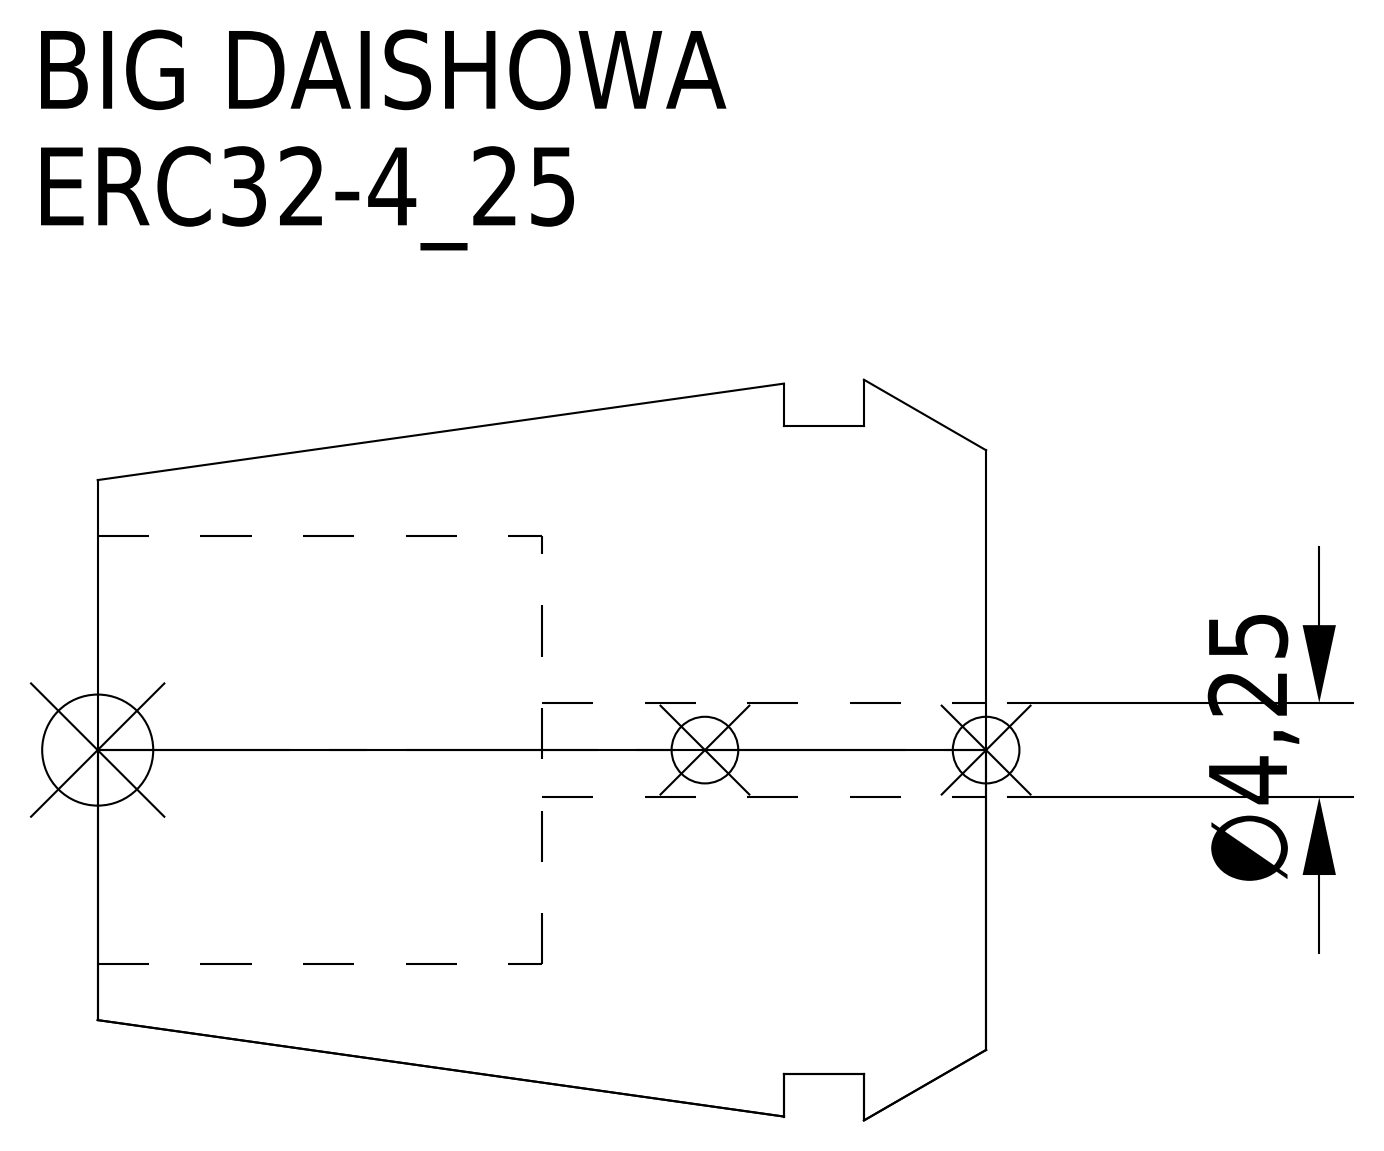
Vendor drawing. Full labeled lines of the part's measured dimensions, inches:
Part name (STEP PRODUCT): ERC32-4_25
STEP written by: CREO PARAMETRIC BY PTC INC, 2016380 (AUTOMOTIVE_DESIGN)
Units: inches
Bodies: 1 solid, 15 faces (5 planar, 6 cylindrical, 4 other)
Overall size (bounding box): 1.575 × 1.313 × 1.313
Volume: 1.239 in³ · Surface area: 10.26 in²
Round holes (diameter × count): ⌀0.167 ×1, ⌀0.76 ×1
Round bosses / shafts (diameter × count): ⌀1.15 ×1
Main face-to-face distances: 0.787, 0.217, 0.571, 0.358, 0.142, 0.429, 1.575, 1.358, 1.217
